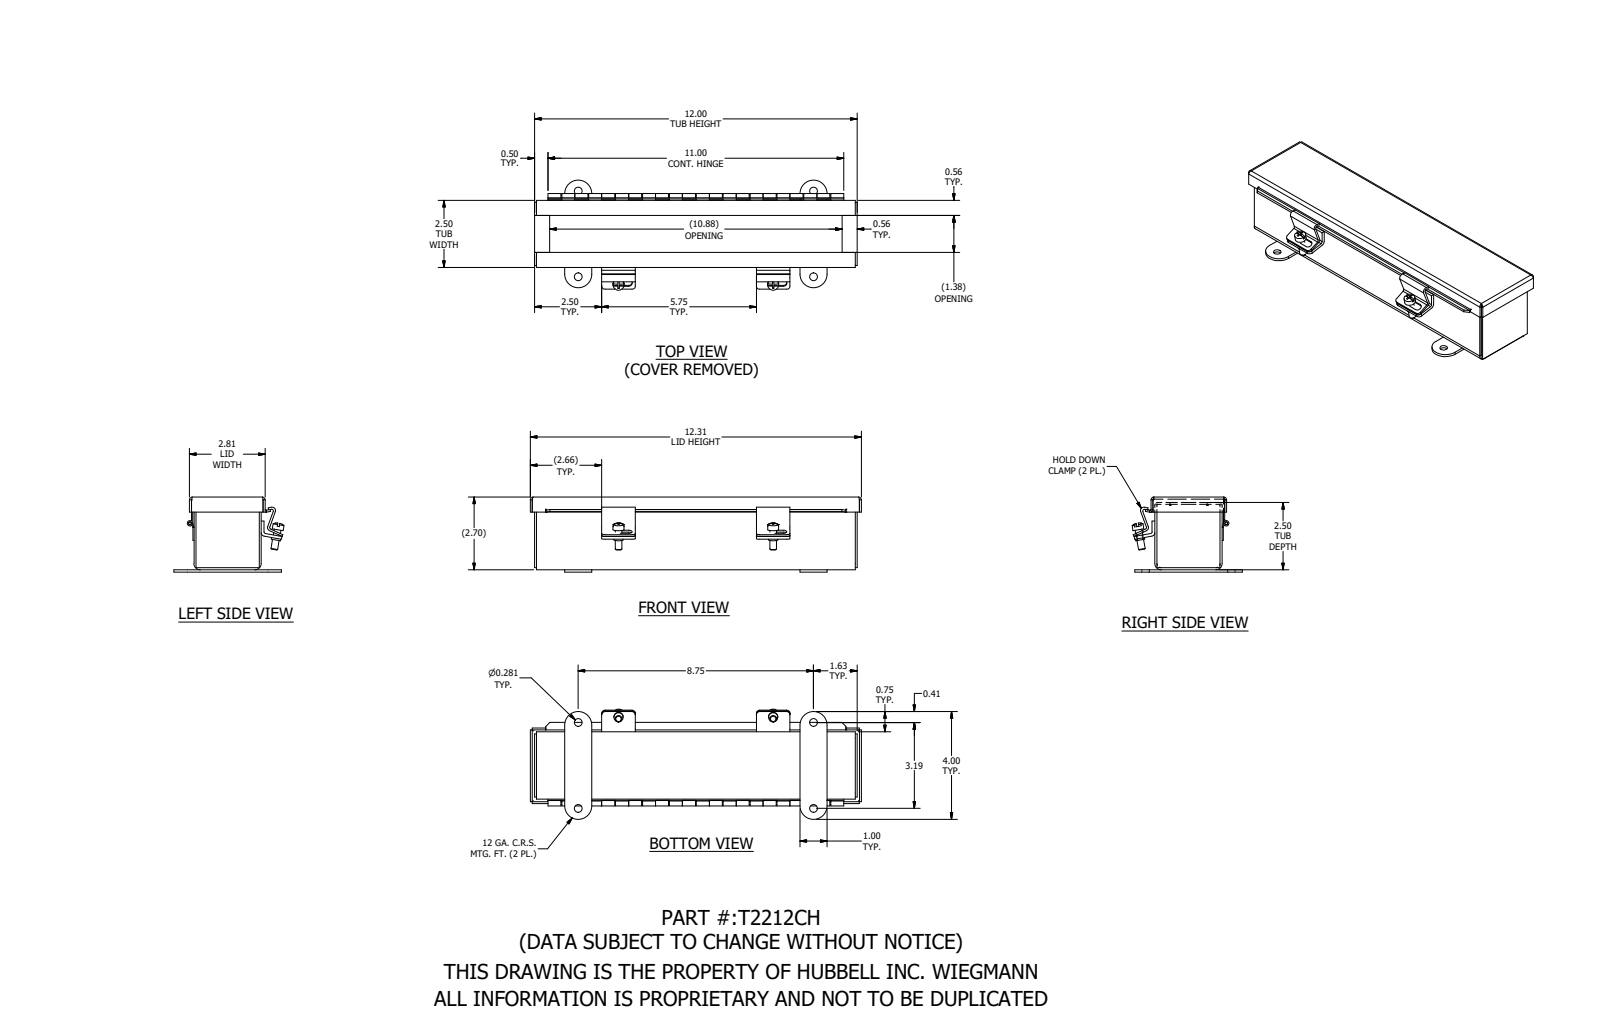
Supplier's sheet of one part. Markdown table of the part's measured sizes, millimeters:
| quantity | value |
| --- | --- |
| part name | T2212CH |
| STEP written by | SolidWorks 2021 (AUTOMOTIVE_DESIGN) |
| units | millimeters |
| bodies | 15 solids, 420 faces (234 planar, 168 cylindrical, 18 other) |
| overall size | 312.8 × 104 × 70.9 |
| volume | 230 100 mm³ |
| surface area | 260 400 mm² |
| round holes (diameter × count) | 7.1 × 4, 5 × 2, 2.9 × 1 |
| round bosses / shafts (diameter × count) | 10.4 × 2, 8.7 × 2, 6.4 × 2, 5.1 × 1, 2.5 × 1 |
| partial cylindrical surfaces (radius × count) | 0.8 × 9, 2.7 × 9, 3.2 × 8, 3.4 × 4, 12.7 × 4, 1.6 × 3, 3.2 × 3, 4 × 2 |
| main face-to-face distances | 1.9, 61.6, 66.7, 63.5, 59.7, 68.6, 65.9, 4.3, 64.8, 5.1 |
| hole center spacings | 80.9, 222.3, 236.6, 146.1 |
